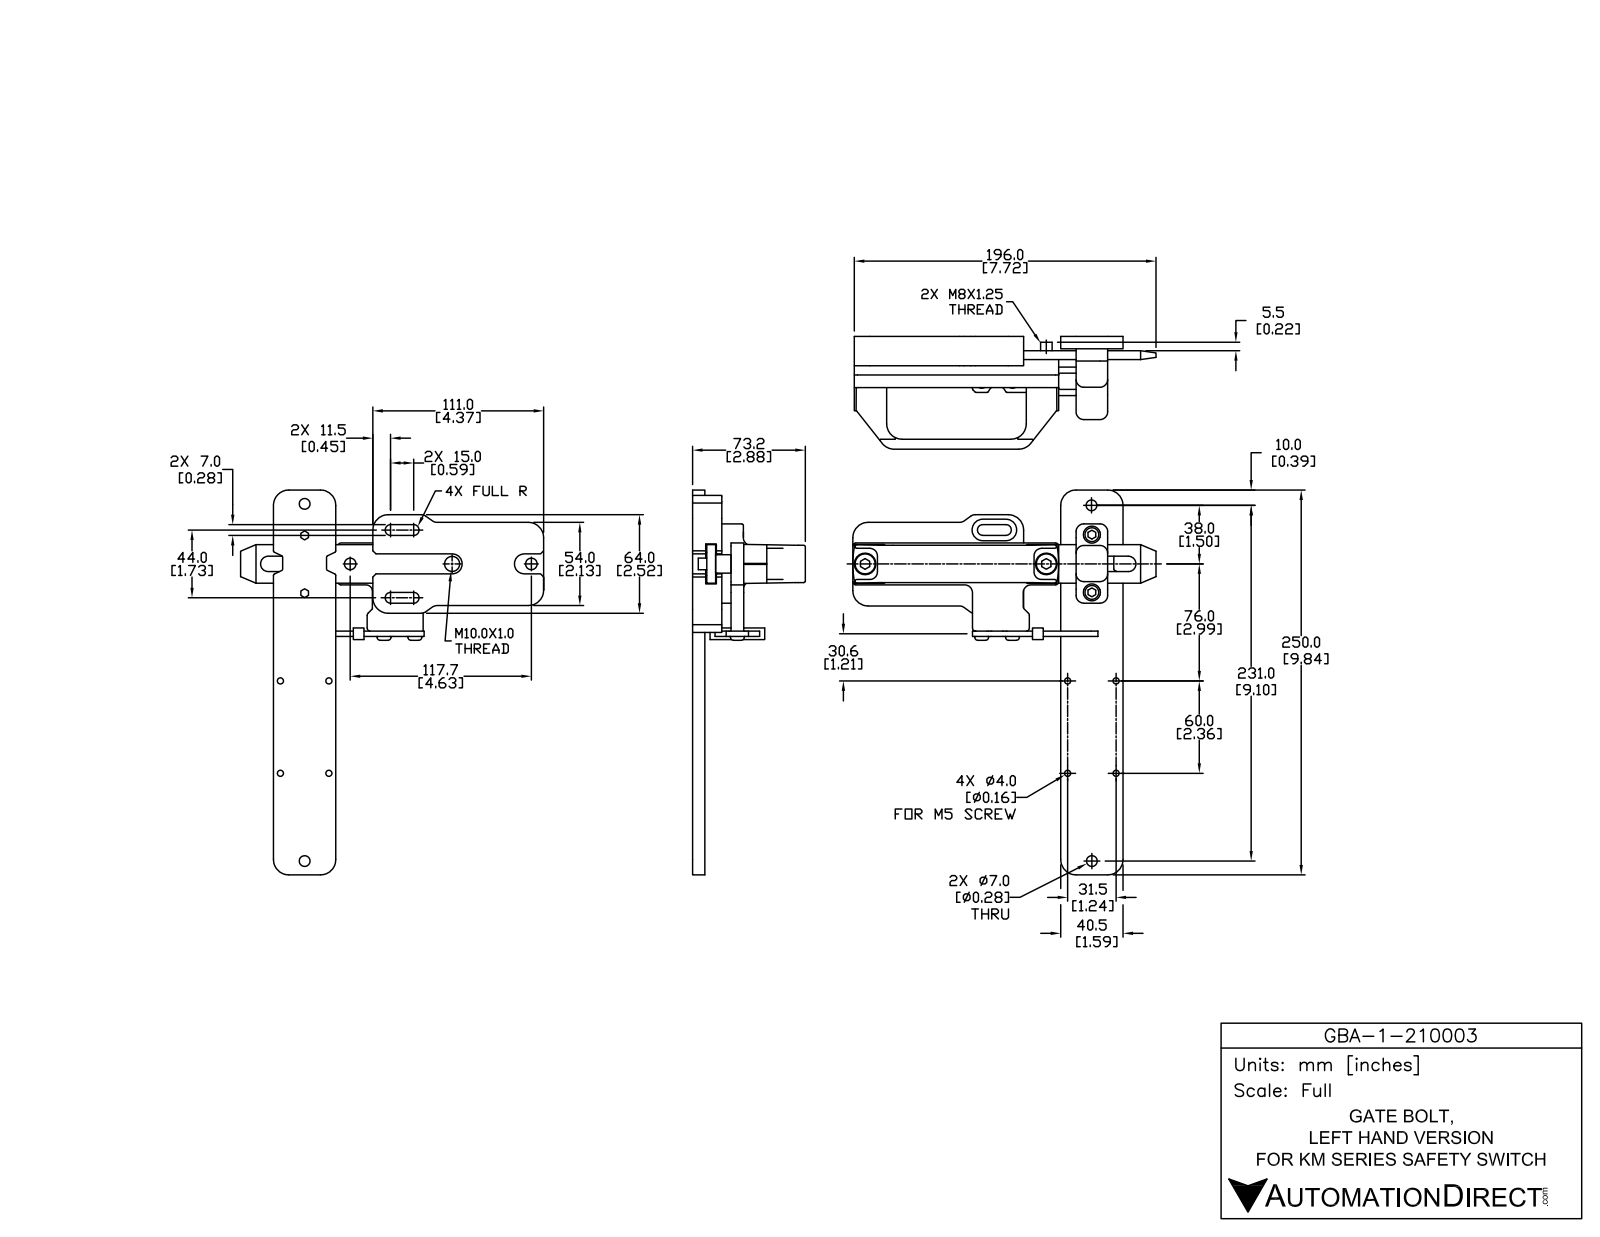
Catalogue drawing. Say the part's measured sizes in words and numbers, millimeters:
The part is named "GBA-1-210003". Its 3-D file was written by "SolidWorks 2019 (AUTOMOTIVE_DESIGN)". It is 15 solids with 860 faces: 308 planar, 351 cylindrical and 201 other. Overall it measures 250 by 248.1 by 78.8 millimeters. Its volume is 306 390 cubic millimeters and its surface area 114 463 square millimeters. Round holes: 4 of diameter 4, 2 of diameter 4.2, 2 of diameter 5, 2 of diameter 5.5, 2 of diameter 6.5, 2 of diameter 6.75, 2 of diameter 6.8, 2 of diameter 8.3, 2 of diameter 8.6, 2 of diameter 8.8, 2 of diameter 11, 2 of diameter 14. Round bosses or shafts: 2 of diameter 13, 2 of diameter 10, 2 of diameter 9.3, 2 of diameter 8, 2 of diameter 6, 2 of diameter 5. Partial cylindrical surfaces (rounded edges, fillets, slot ends): 110 of radius 0.5, 56 of radius 0.1, 38 of radius 1, 16 of radius 3, 16 of radius 5, 14 of radius 2, 8 of radius 8, 6 of radius 3.45. The main face-to-face distances are 8, 23.8, 10, 19, 6, 7.8, 16, 15.8, 13.8, 5.8. The hole center spacings are 20, 30, 57.97, 59.91, 60, 67.08, 95.19, 103.67.
